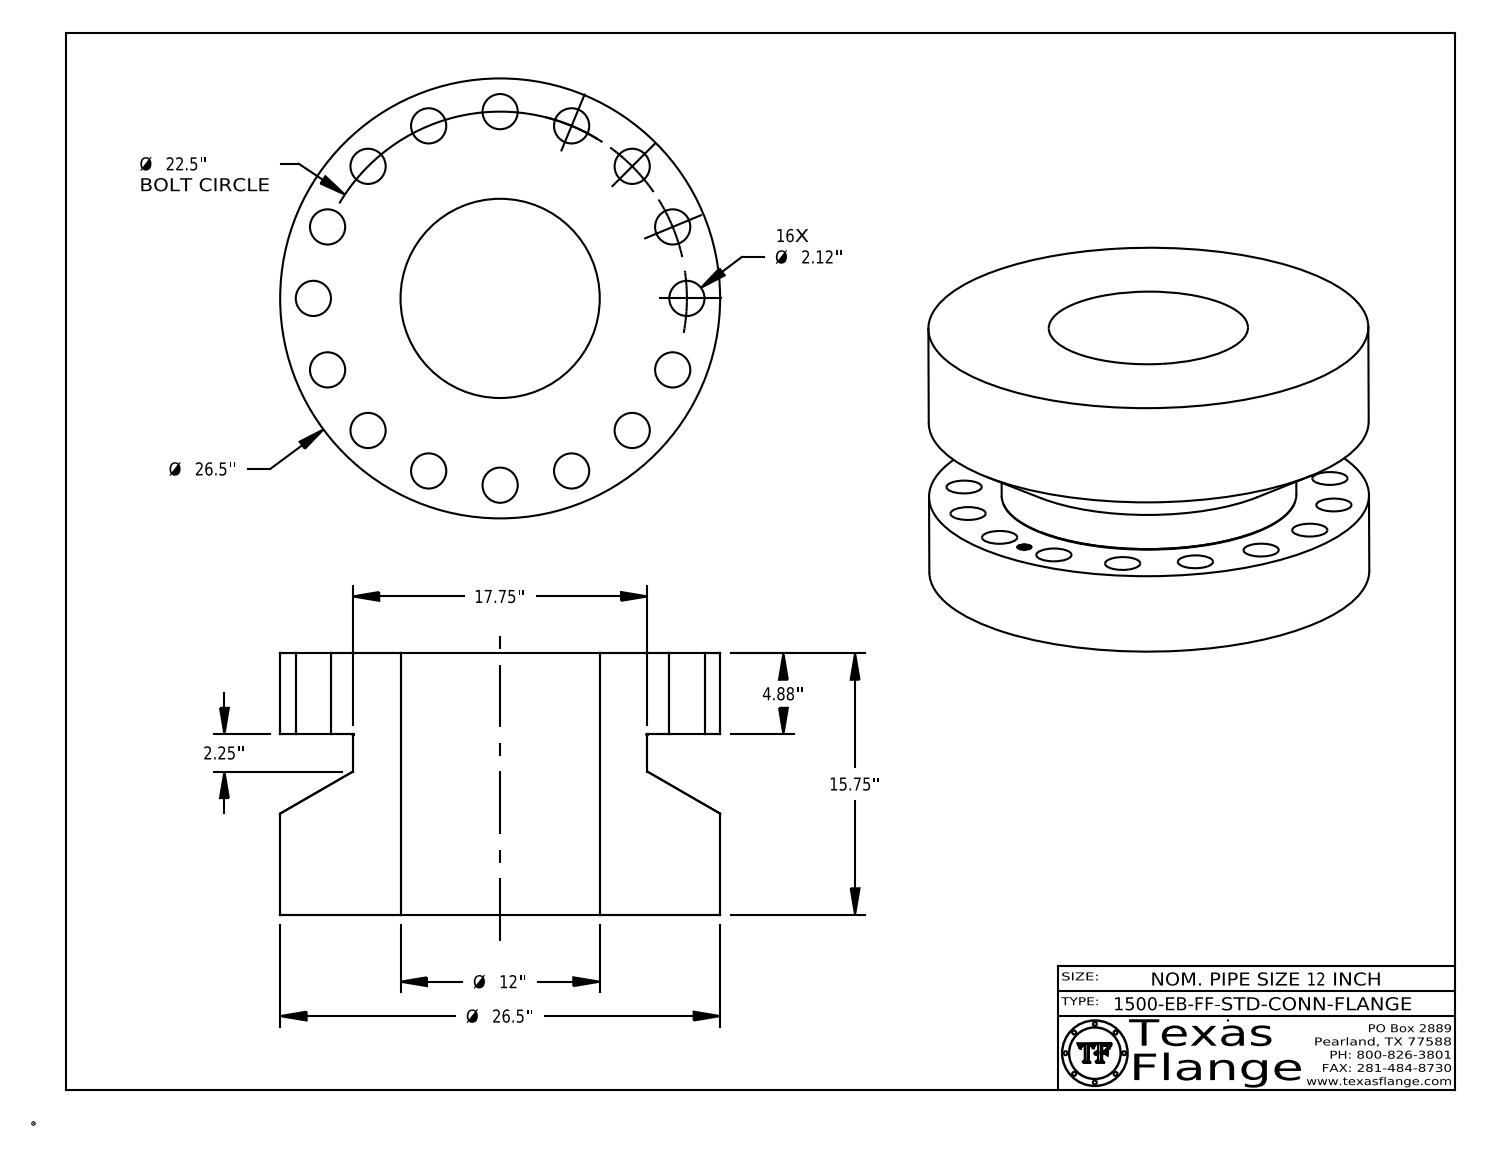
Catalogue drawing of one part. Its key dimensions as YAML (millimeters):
part_name: "12-1500-EB-FF-STD-CONN-FLANGE"
step_written_by: "CATIA V5 STEP AP214 (AUTOMOTIVE_DESIGN)"
units: millimeters
bodies: {solids: 1, faces: 434, planar: 368, cylindrical: 60, other: 6}
overall_size: [673.1, 673.1, 400.1]
volume: 90720000
surface_area: 2306000
round_holes:
  - {diameter: 53.8, count: 16}
  - {diameter: 21.6, count: 1}
  - {diameter: 304.8, count: 1}
round_bosses_or_shafts:
  - {diameter: 1.3, count: 8}
  - {diameter: 673.1, count: 1}
  - {diameter: 450.9, count: 1}
  - {diameter: 17, count: 1}
face_to_face_distances: [400.1, 124, 276.1, 123.8, 276.2, 0.4, 6.5, 6.3, 1.2, 4.2]
hole_center_spacings: [317.5, 528, 560.5, 285.8, 218.7, 404.1, 111.5, 111.5]
